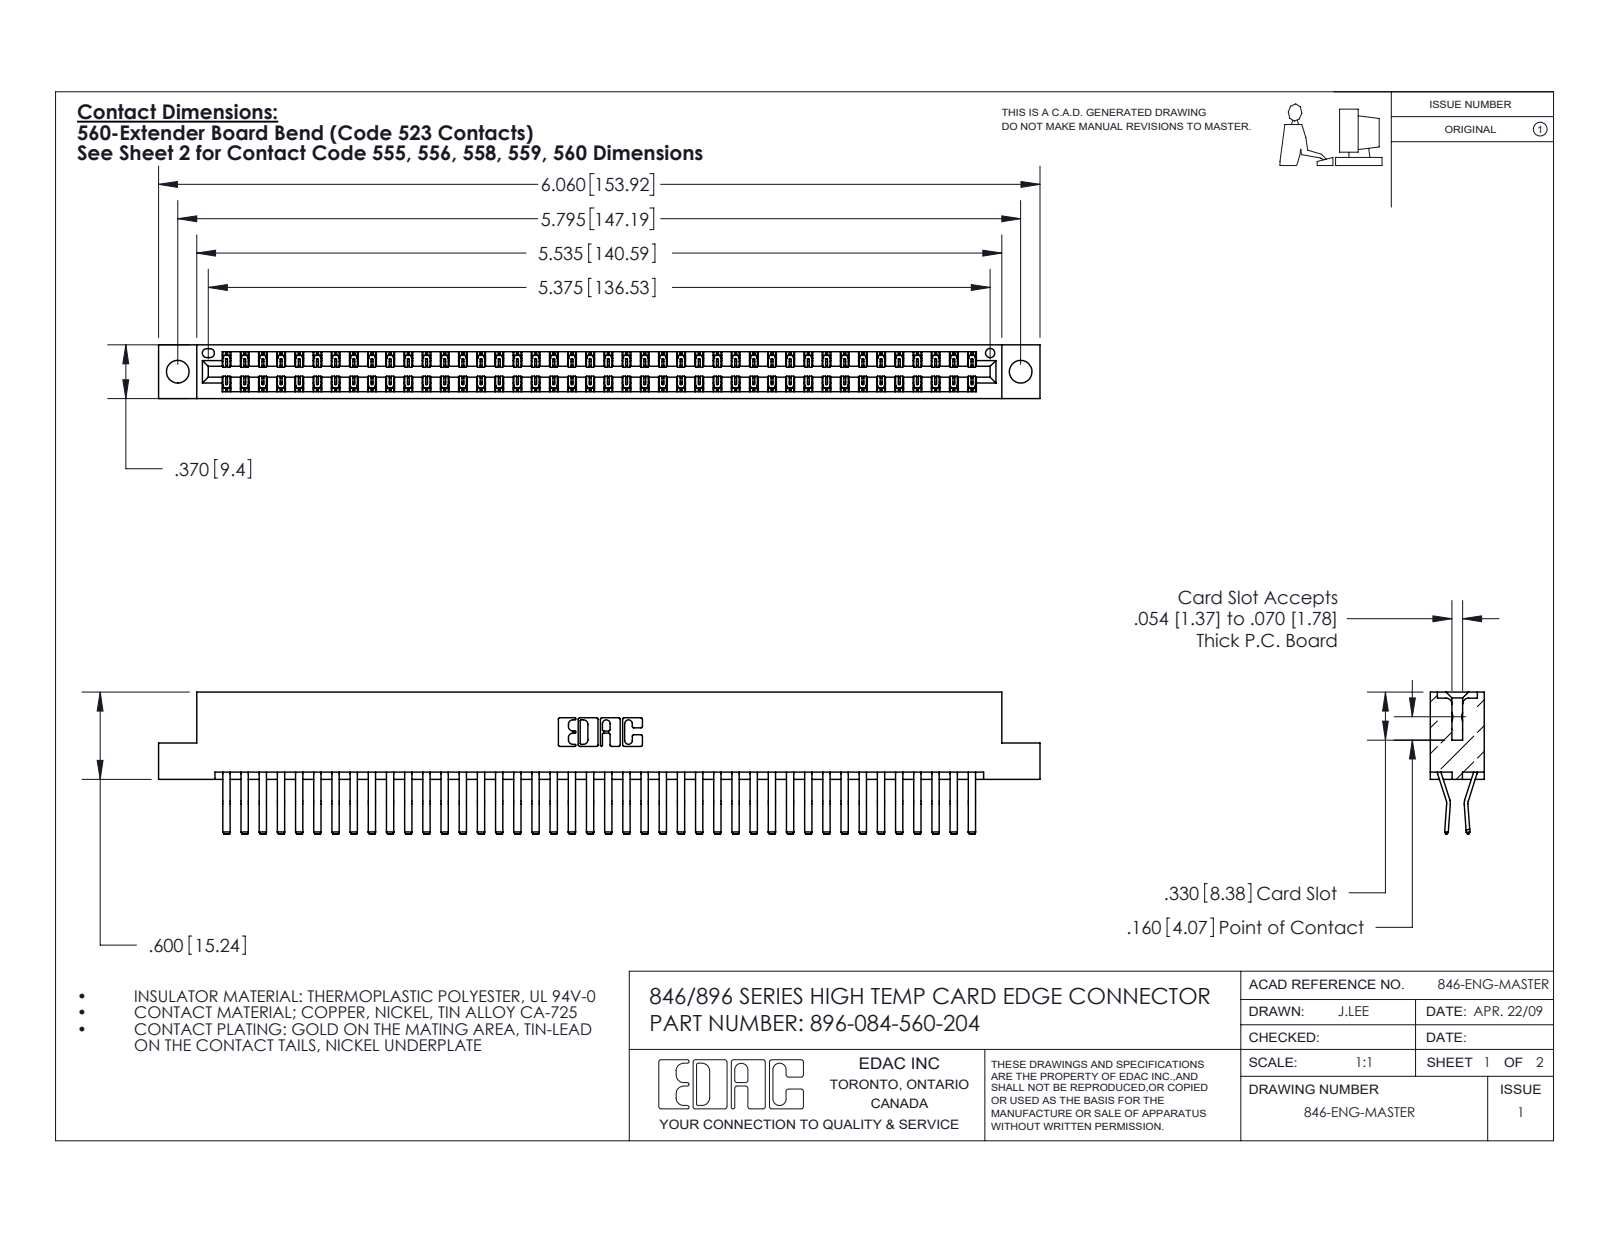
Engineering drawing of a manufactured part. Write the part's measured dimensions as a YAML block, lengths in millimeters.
part_name: "345-292-001_560 Tail; 396-084-560-204; 346 Part_Flush Mounting Lugs - 0.156 Dia-TH"
step_written_by: "SolidWorks 2016 (CONFIG_CONTROL_DESIGN)"
units: millimeters
bodies: {solids: 85, faces: 4658, planar: 3016, cylindrical: 1642, other: 0}
overall_size: [153.9, 24.8, 9.4]
volume: 15500
surface_area: 22550
round_holes:
  - {diameter: 4, count: 2}
  - {diameter: 1.6, count: 1}
partial_cylinders:
  - {radius: 0.2, count: 126}
  - {radius: 0.3, count: 22}
  - {radius: 0.2, count: 6}
  - {radius: 0.8, count: 6}
  - {radius: 0.7, count: 3}
  - {radius: 0.3, count: 2}
  - {radius: 0.4, count: 2}
  - {radius: 0.6, count: 2}
face_to_face_distances: [1.2, 8.2, 9.4, 0.6, 6.4, 1.8, 7.6, 7, 3.8, 5.6]
hole_center_spacings: [6.2, 141.9, 147.2]
